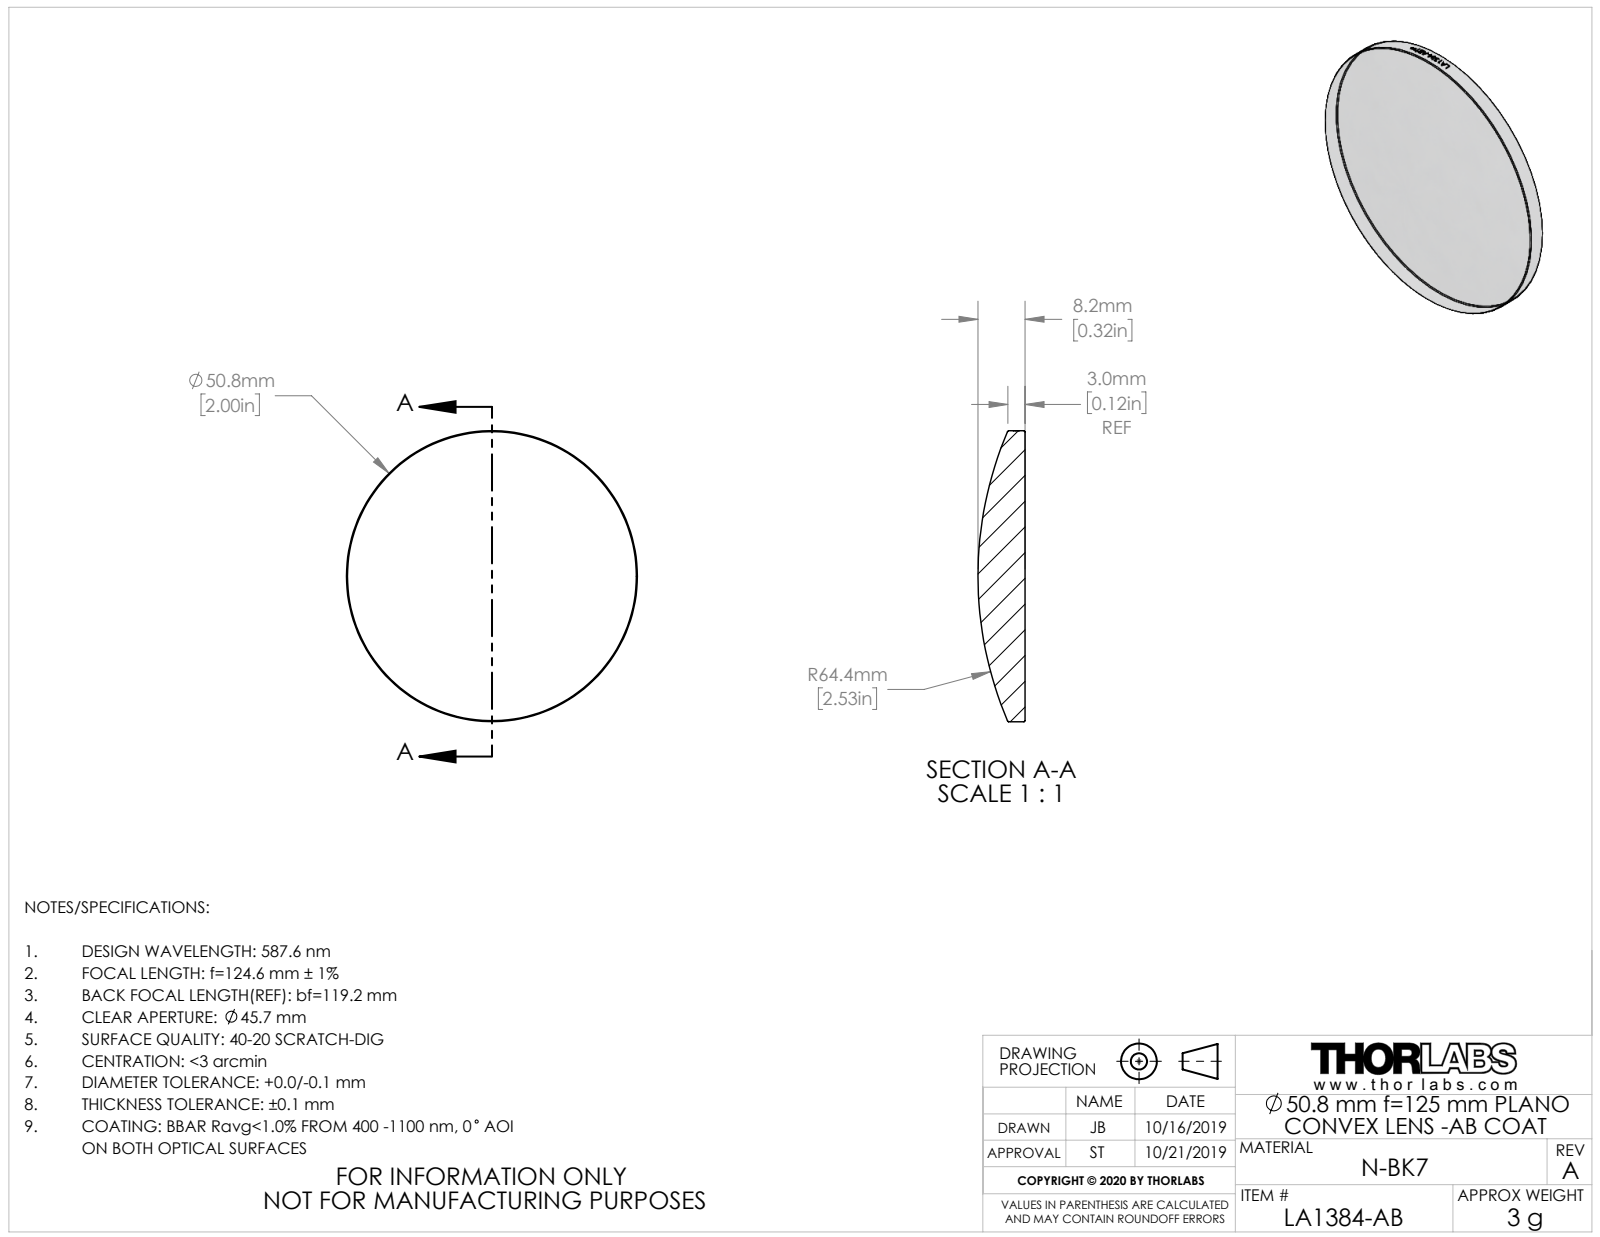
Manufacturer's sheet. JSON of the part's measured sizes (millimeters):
{"part_name": "TTN195802-E0W", "step_written_by": "SolidWorks 2018 (CONFIG_CONTROL_DESIGN)", "units": "millimeters", "bodies": {"solids": 1, "faces": 29, "planar": 1, "cylindrical": 22, "other": 6}, "overall_size": [50.8, 50.8, 8.22], "volume_mm3": 11439, "surface_area_mm2": 4594, "round_bosses_or_shafts": [[50.8, 1]]}
